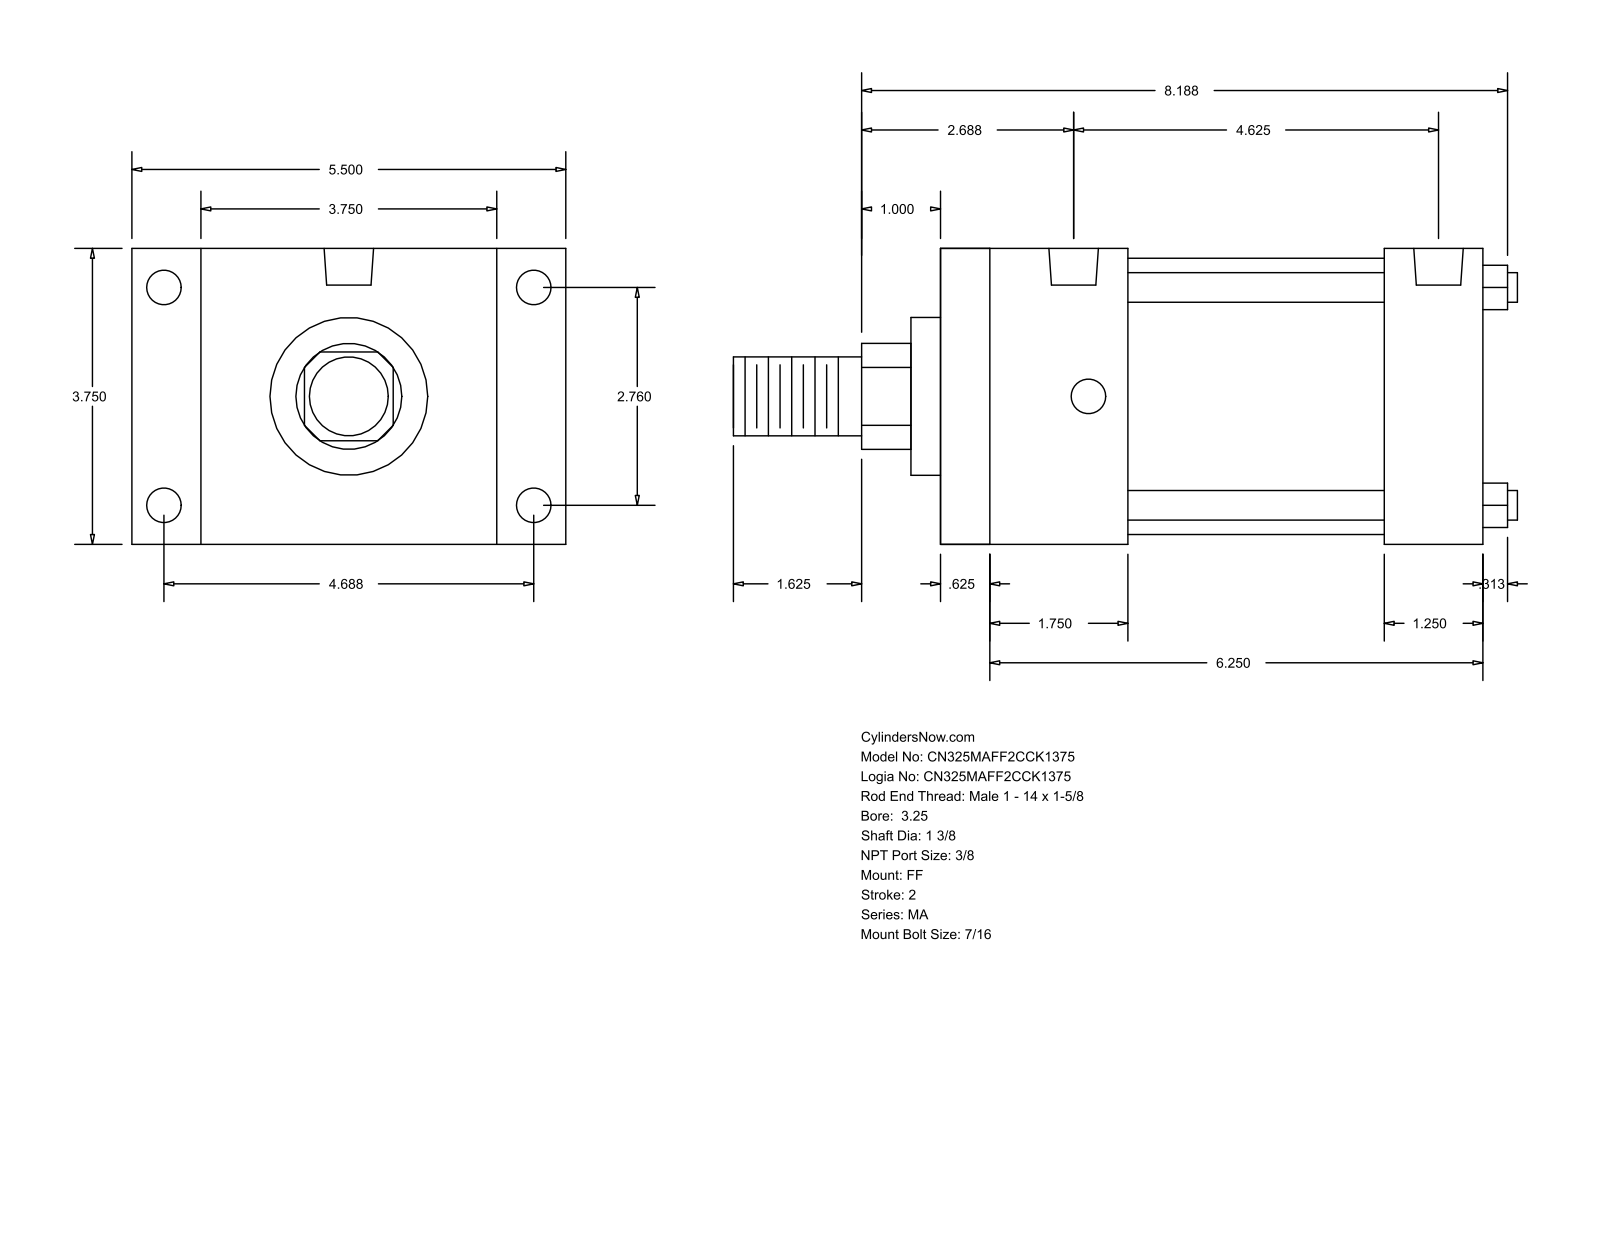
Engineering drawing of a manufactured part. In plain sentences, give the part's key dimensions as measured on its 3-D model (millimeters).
The part is named "MA_FF__0325_1.375". Its 3-D file was written by "GSSL Pune (CONFIG_CONTROL_DESIGN)". It is 0 solids with 92 faces: 64 planar, 28 cylindrical and 0 other. Overall it measures 252.41 by 139.7 by 95.25 millimeters. Round holes: 8 of diameter 11.11, 2 of diameter 15.93. Round bosses or shafts: 4 of diameter 9.53, 1 of diameter 88.9, 1 of diameter 50.8, 1 of diameter 34.92, 1 of diameter 25.4. Partial cylindrical surfaces (rounded edges, fillets, slot ends): 1 of radius 17.06. The main face-to-face distances are 95.24, 174.63, 15.87, 158.76, 22.23, 117.47, 60.32, 142.88, 44.45, 127.01. The hole center spacings are 4.77, 70.1, 107.94, 112.71, 119.06, 138.16, 117.48.
